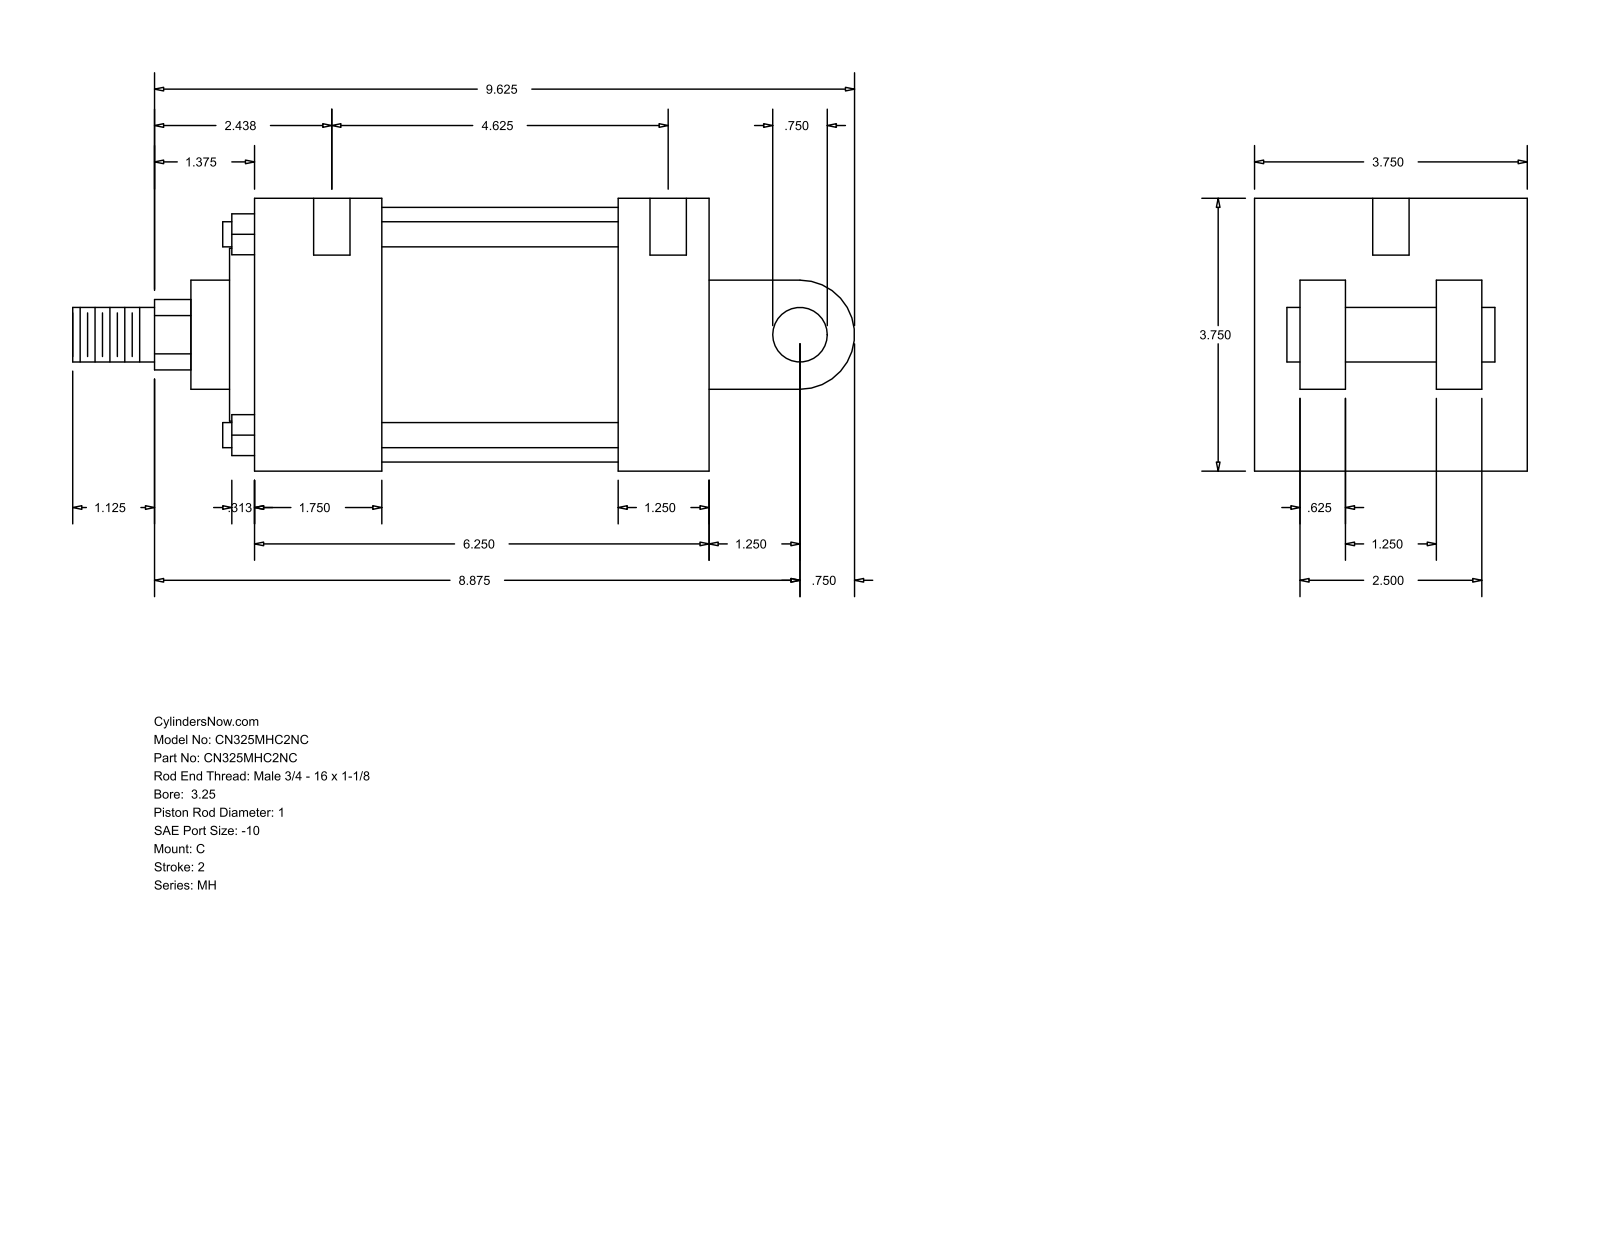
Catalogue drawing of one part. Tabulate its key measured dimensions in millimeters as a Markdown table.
| quantity | value |
| --- | --- |
| part name | MH_C__0325_1 |
| STEP written by | GSSL Pune (CONFIG_CONTROL_DESIGN) |
| units | millimeters |
| bodies | 0 solids, 101 faces (71 planar, 30 cylindrical, 0 other) |
| overall size | 273.05 × 95.25 × 95.25 |
| round holes (diameter × count) | 5.56 × 4, 12.7 × 2 |
| round bosses / shafts (diameter × count) | 8.76 × 4, 19.05 × 2, 88.9 × 1, 60.33 × 1, 38.1 × 1, 25.4 × 1 |
| partial cylindrical surfaces (radius × count) | 12.29 × 1, 19.05 × 1 |
| main face-to-face distances | 95.24, 15.87, 158.76, 63.5, 79.37, 31.74, 47.63, 44.46, 127.01, 82.55 |
| hole center spacings | 123.82, 1.58, 4.76, 117.48, 119.06, 122.24 |
